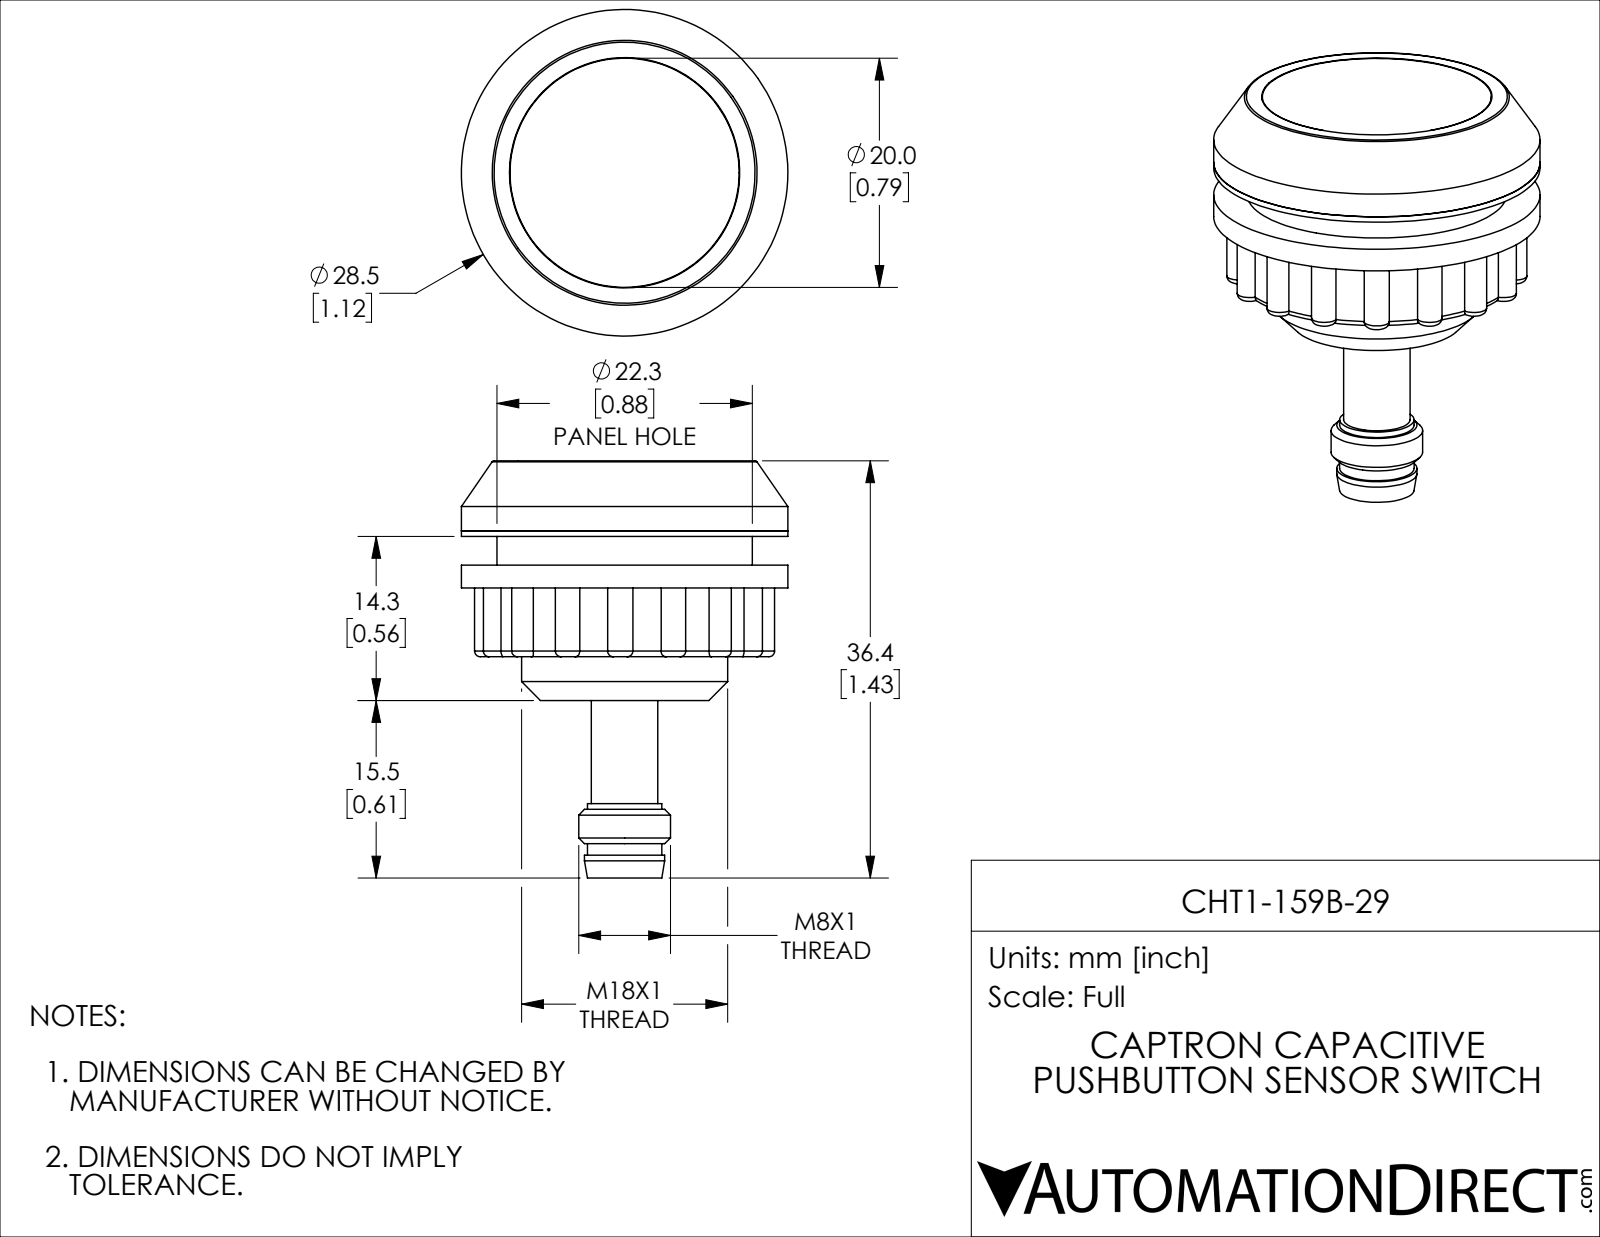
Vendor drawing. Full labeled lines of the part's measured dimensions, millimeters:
Part name (STEP PRODUCT): CHT1-159B-29
STEP written by: SolidWorks 2019 (CONFIG_CONTROL_DESIGN)
Units: millimetres
Bodies: 10 solids, 195 faces (26 planar, 93 cylindrical, 76 other)
Overall size (bounding box): 36.42 × 28.5 × 28.5
Volume: 10 064 mm³ · Surface area: 7 455 mm²
Round holes (diameter × count): ⌀6 ×1, ⌀14.7 ×1, ⌀17 ×1, ⌀20.1 ×1, ⌀22.3 ×1, ⌀22.6 ×1
Round bosses / shafts (diameter × count): ⌀1 ×5, ⌀28.5 ×1, ⌀18 ×1, ⌀14.4 ×1, ⌀8 ×1, ⌀7 ×1, ⌀6.5 ×1, ⌀5.8 ×1
Partial cylindrical surfaces — rounded edges, fillets, slot ends (radius × count): R1.1 ×16, R12 ×1
Main face-to-face distances: 3, 6.08, 6.58, 3.85, 3.08, 0.77, 2.23, 10.5, 2, 4
